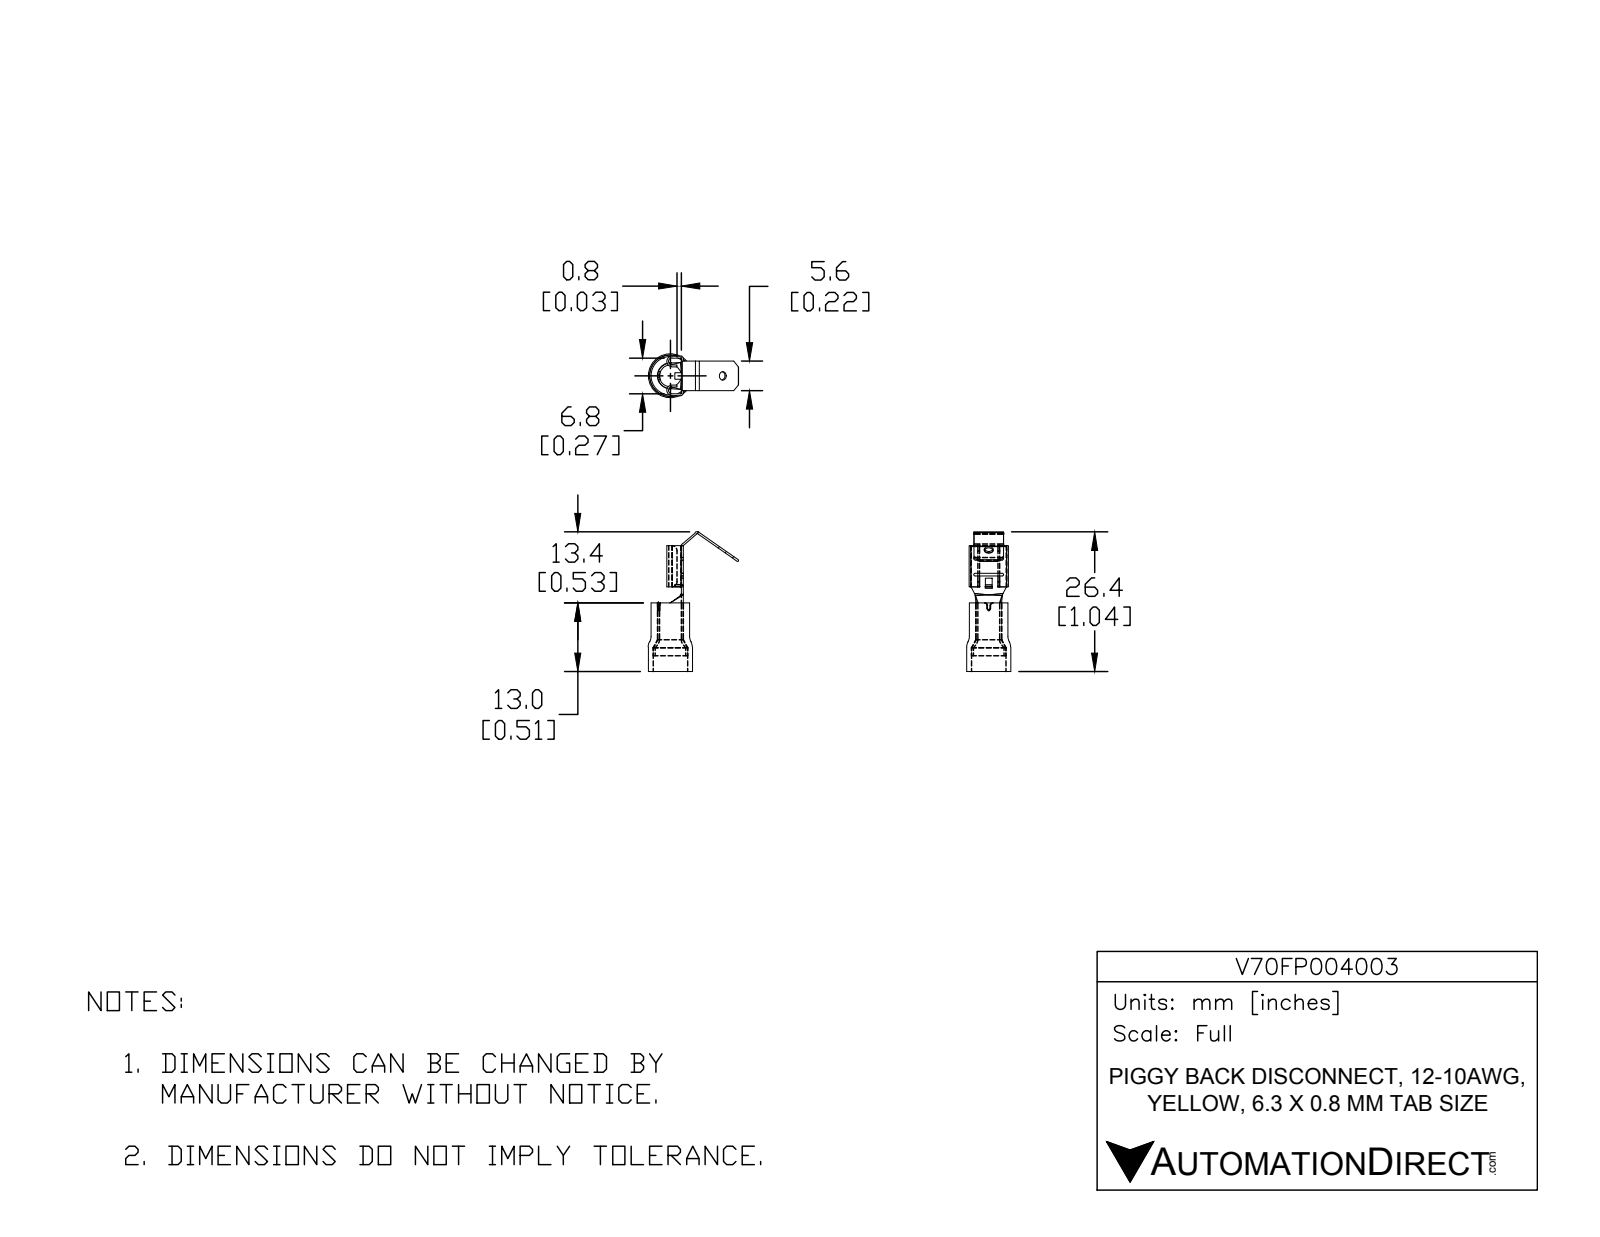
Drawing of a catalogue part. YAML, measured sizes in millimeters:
part_name: "V70FP004003"
step_written_by: "SolidWorks 2017 (AUTOMOTIVE_DESIGN)"
units: millimeters
bodies: {solids: 2, faces: 123, planar: 49, cylindrical: 48, other: 26}
overall_size: [26.42, 17.06, 8.35]
volume: 432
surface_area: 1393
round_holes:
  - {diameter: 1.6, count: 1}
  - {diameter: 4.13, count: 1}
  - {diameter: 5.8, count: 1}
  - {diameter: 6.5, count: 1}
round_bosses_or_shafts:
  - {diameter: 8.35, count: 1}
  - {diameter: 7.3, count: 1}
  - {diameter: 4.83, count: 1}
partial_cylinders:
  - {radius: 0.25, count: 8}
  - {radius: 0.5, count: 4}
  - {radius: 1, count: 4}
  - {radius: 0.38, count: 2}
  - {radius: 0.6, count: 2}
  - {radius: 0.65, count: 2}
face_to_face_distances: [0.35, 1.65, 5.46, 7.11, 13, 2, 5.81, 1.3, 5.11, 3.81]
